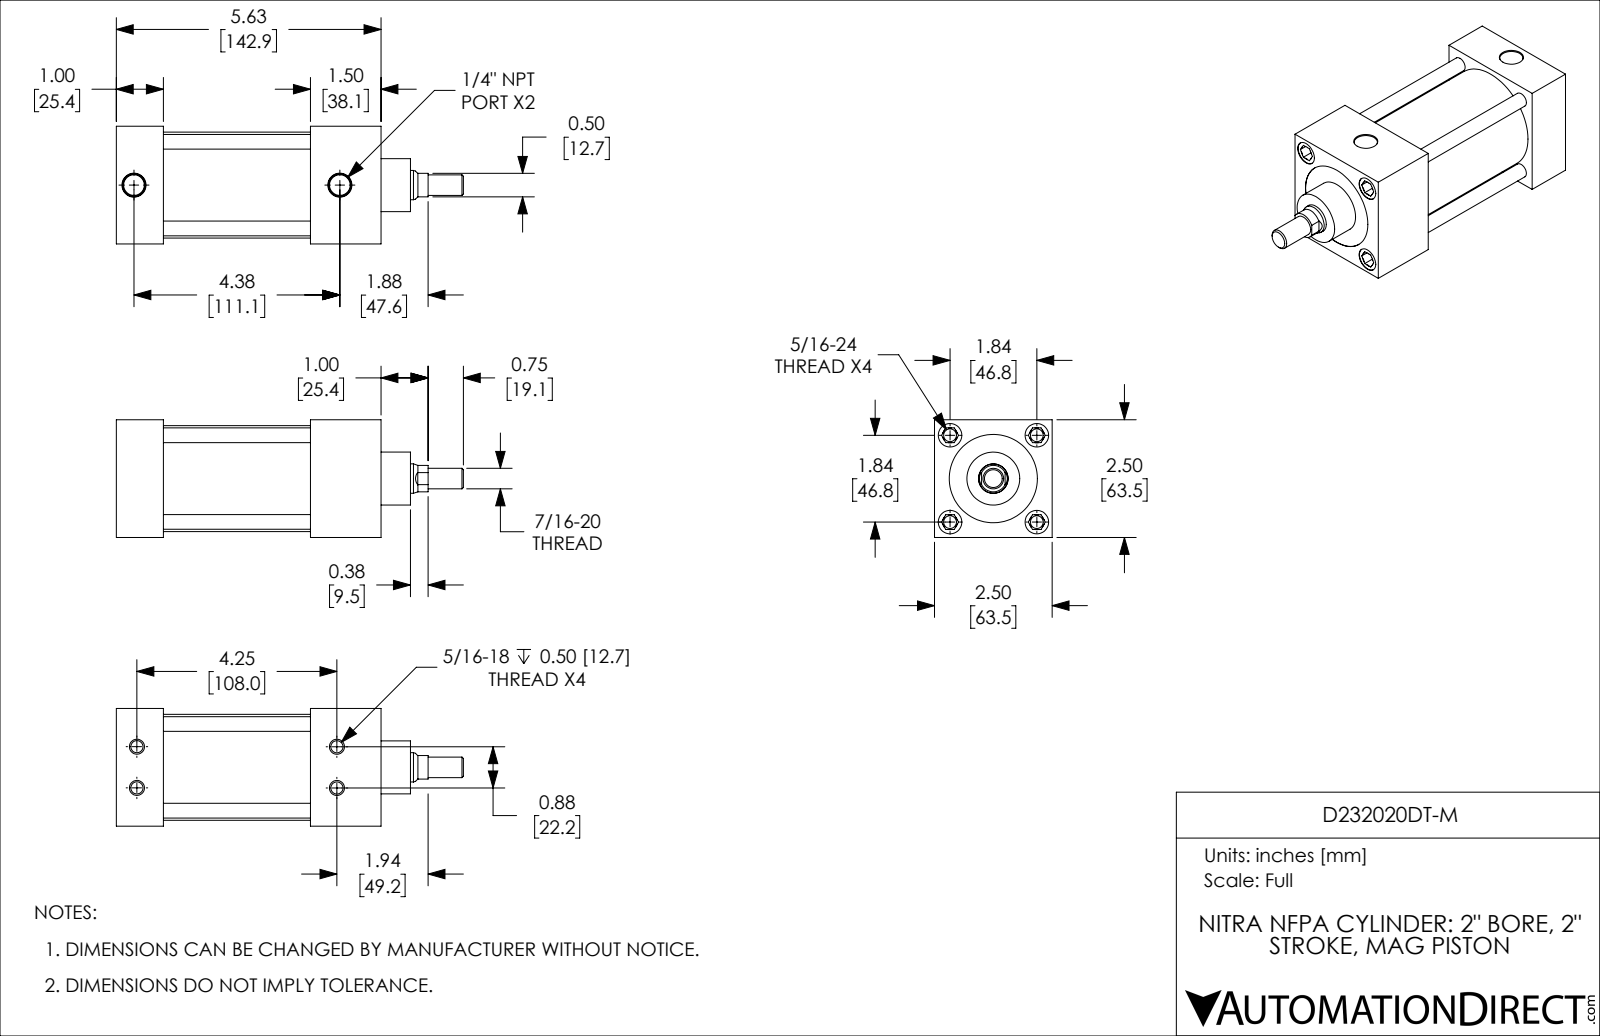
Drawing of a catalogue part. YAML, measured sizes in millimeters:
part_name: "D232020DT-M_BODY; D232020DT-M_PISTON_KK1; D232020DT-M"
step_written_by: "SolidWorks 2019 (CONFIG_CONTROL_DESIGN)"
units: millimeters
bodies: {solids: 2, faces: 200, planar: 58, cylindrical: 62, other: 80}
overall_size: [187.3, 63.5, 63.5]
volume: 382600
surface_area: 90520
round_holes:
  - {diameter: 6.9, count: 7}
  - {diameter: 6.5, count: 4}
  - {diameter: 12.7, count: 4}
  - {diameter: 11.1, count: 2}
  - {diameter: 15.9, count: 1}
  - {diameter: 47.6, count: 1}
  - {diameter: 50.8, count: 1}
round_bosses_or_shafts:
  - {diameter: 7.9, count: 4}
  - {diameter: 57.2, count: 1}
  - {diameter: 50.8, count: 1}
  - {diameter: 28.6, count: 1}
  - {diameter: 15.8, count: 1}
  - {diameter: 11.1, count: 1}
partial_cylinders:
  - {radius: 7.1, count: 1}
face_to_face_distances: [63.5, 25.4, 104.8, 79.4, 54, 28.6, 50.8, 142.9, 117.5, 88.9]
hole_center_spacings: [46.7, 46.8, 33, 11.2, 11.3, 22.2, 33.1, 66.1]
